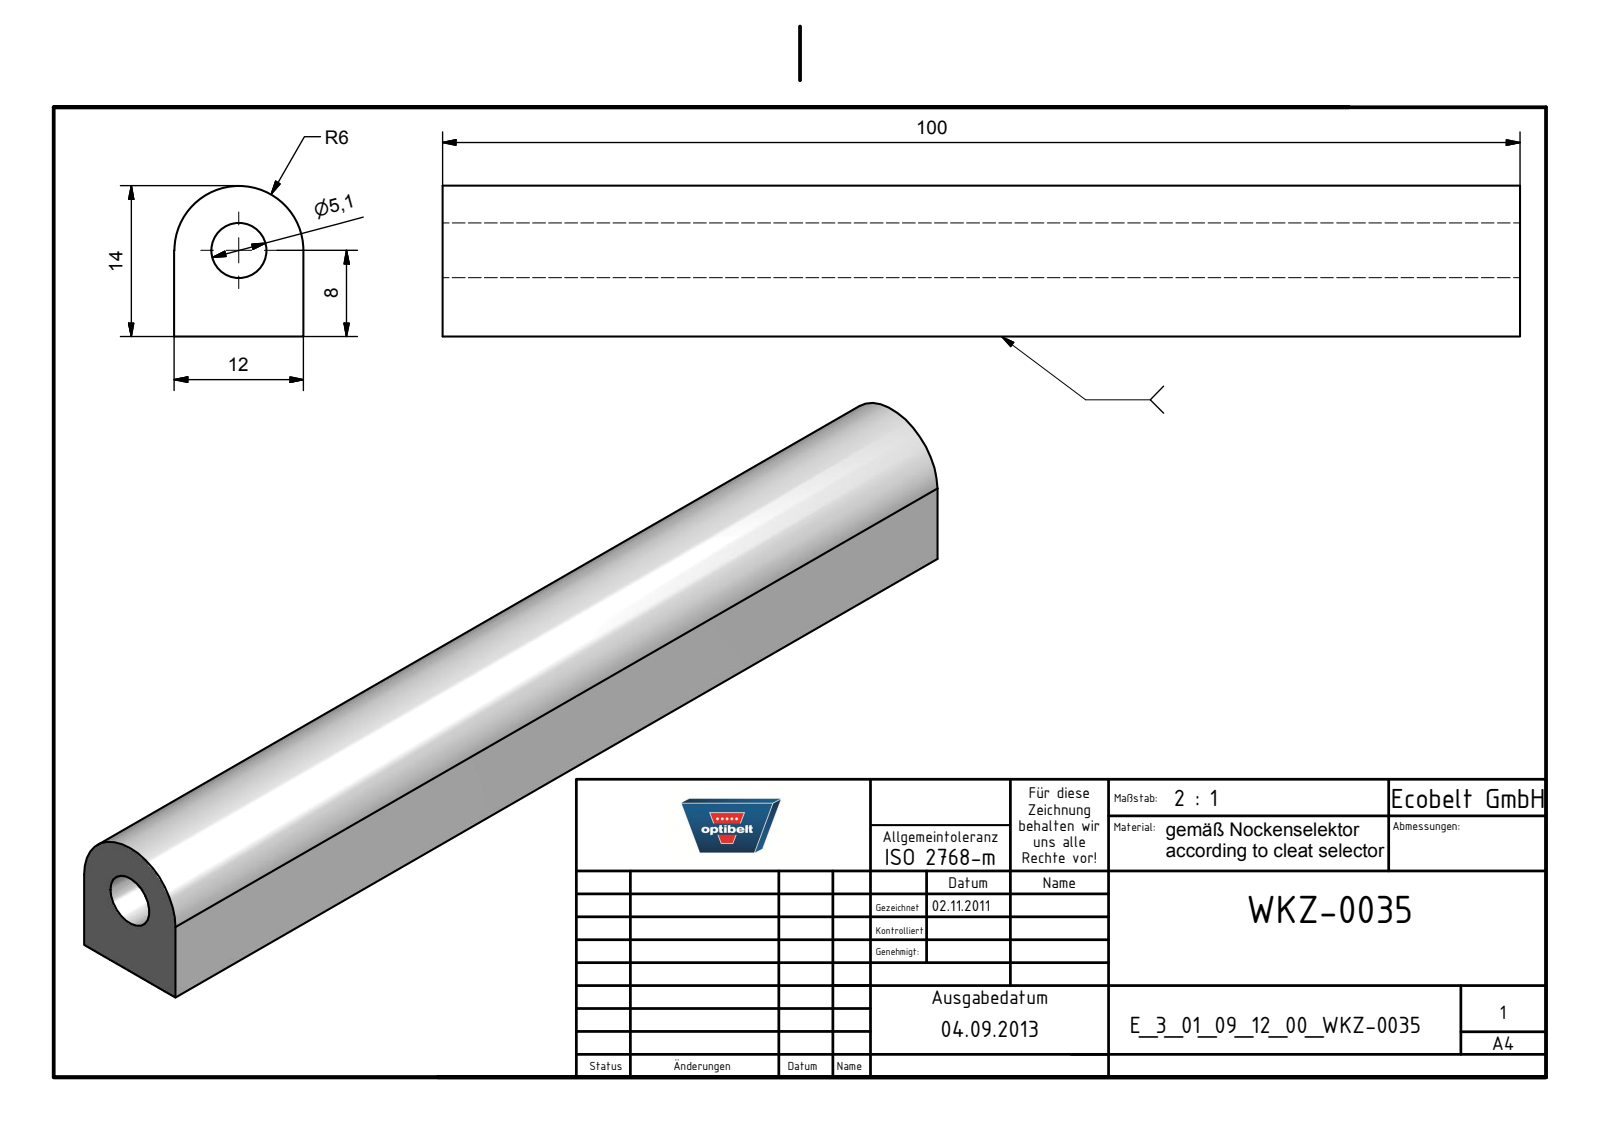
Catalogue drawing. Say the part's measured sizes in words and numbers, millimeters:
The part is named "E_3_01_09_12_00_WKZ-0035". Its 3-D file was written by "Autodesk Inventor 2021 (AUTOMOTIVE_DESIGN)". It is 1 solid with 7 faces: 5 planar, 2 cylindrical and 0 other. Overall it measures 100 by 14 by 12 millimeters. Its volume is 13 212 cubic millimeters and its surface area 6 551 square millimeters. Round holes: 1 of diameter 5.1. Partial cylindrical surfaces (rounded edges, fillets, slot ends): 1 of radius 6. The main face-to-face distances are 12, 100.
